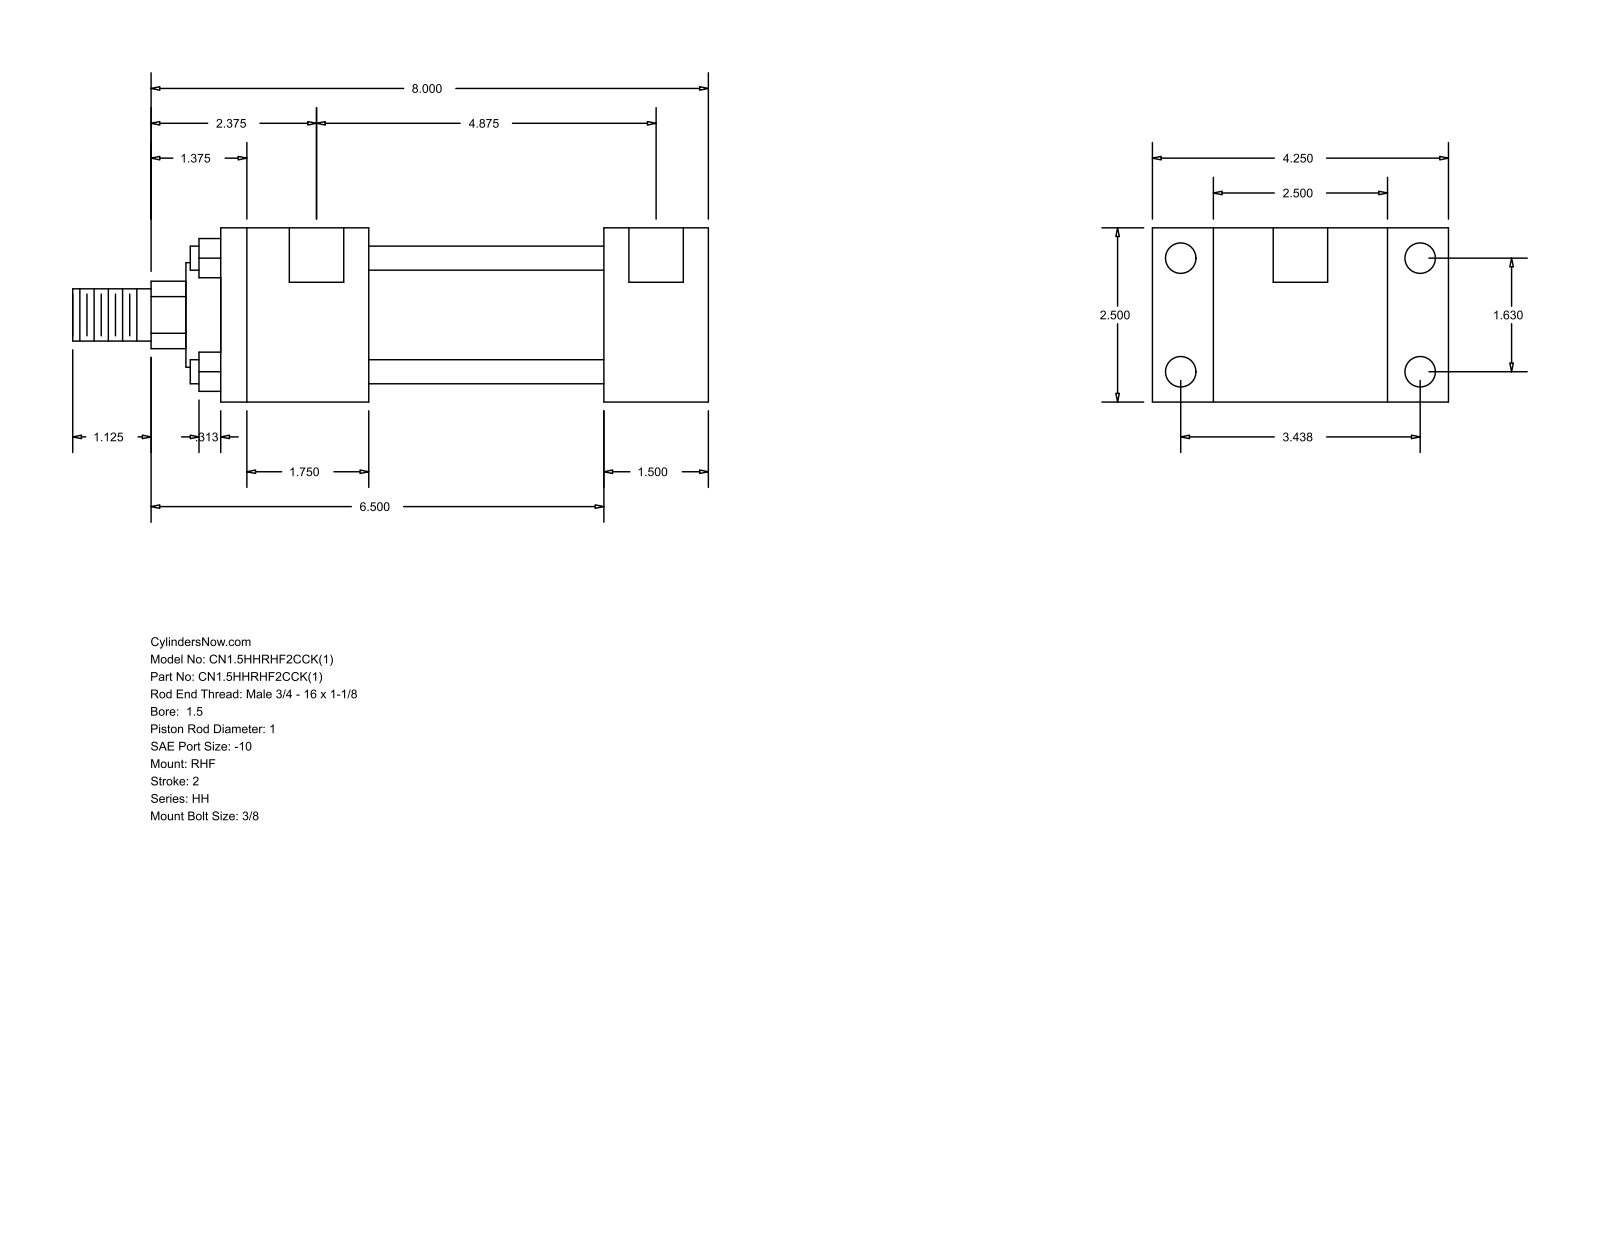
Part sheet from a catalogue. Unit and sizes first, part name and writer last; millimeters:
Units: millimetres
Overall size (bounding box): 231.78 × 107.95 × 63.5
Round holes (diameter × count): ⌀5.56 ×4, ⌀11.13 ×4, ⌀19.84 ×2
Round bosses / shafts (diameter × count): ⌀8.76 ×4, ⌀44.45 ×1, ⌀38.1 ×1, ⌀25.4 ×1, ⌀19.05 ×1
Partial cylindrical surfaces — rounded edges, fillets, slot ends (radius × count): R12.29 ×1
Main face-to-face distances: 63.5, 22.23, 85.73, 38.1, 107.96, 85.72, 123.82, 53.98, 139.7, 177.8
Hole centre spacings: 1.59, 41.4, 87.32, 96.64, 125.41, 127, 123.82
Bodies: 0 solids, 88 faces (60 planar, 28 cylindrical, 0 other)
Part name (STEP PRODUCT): HH_RHF__0150_1
STEP written by: GSSL Pune (CONFIG_CONTROL_DESIGN)
